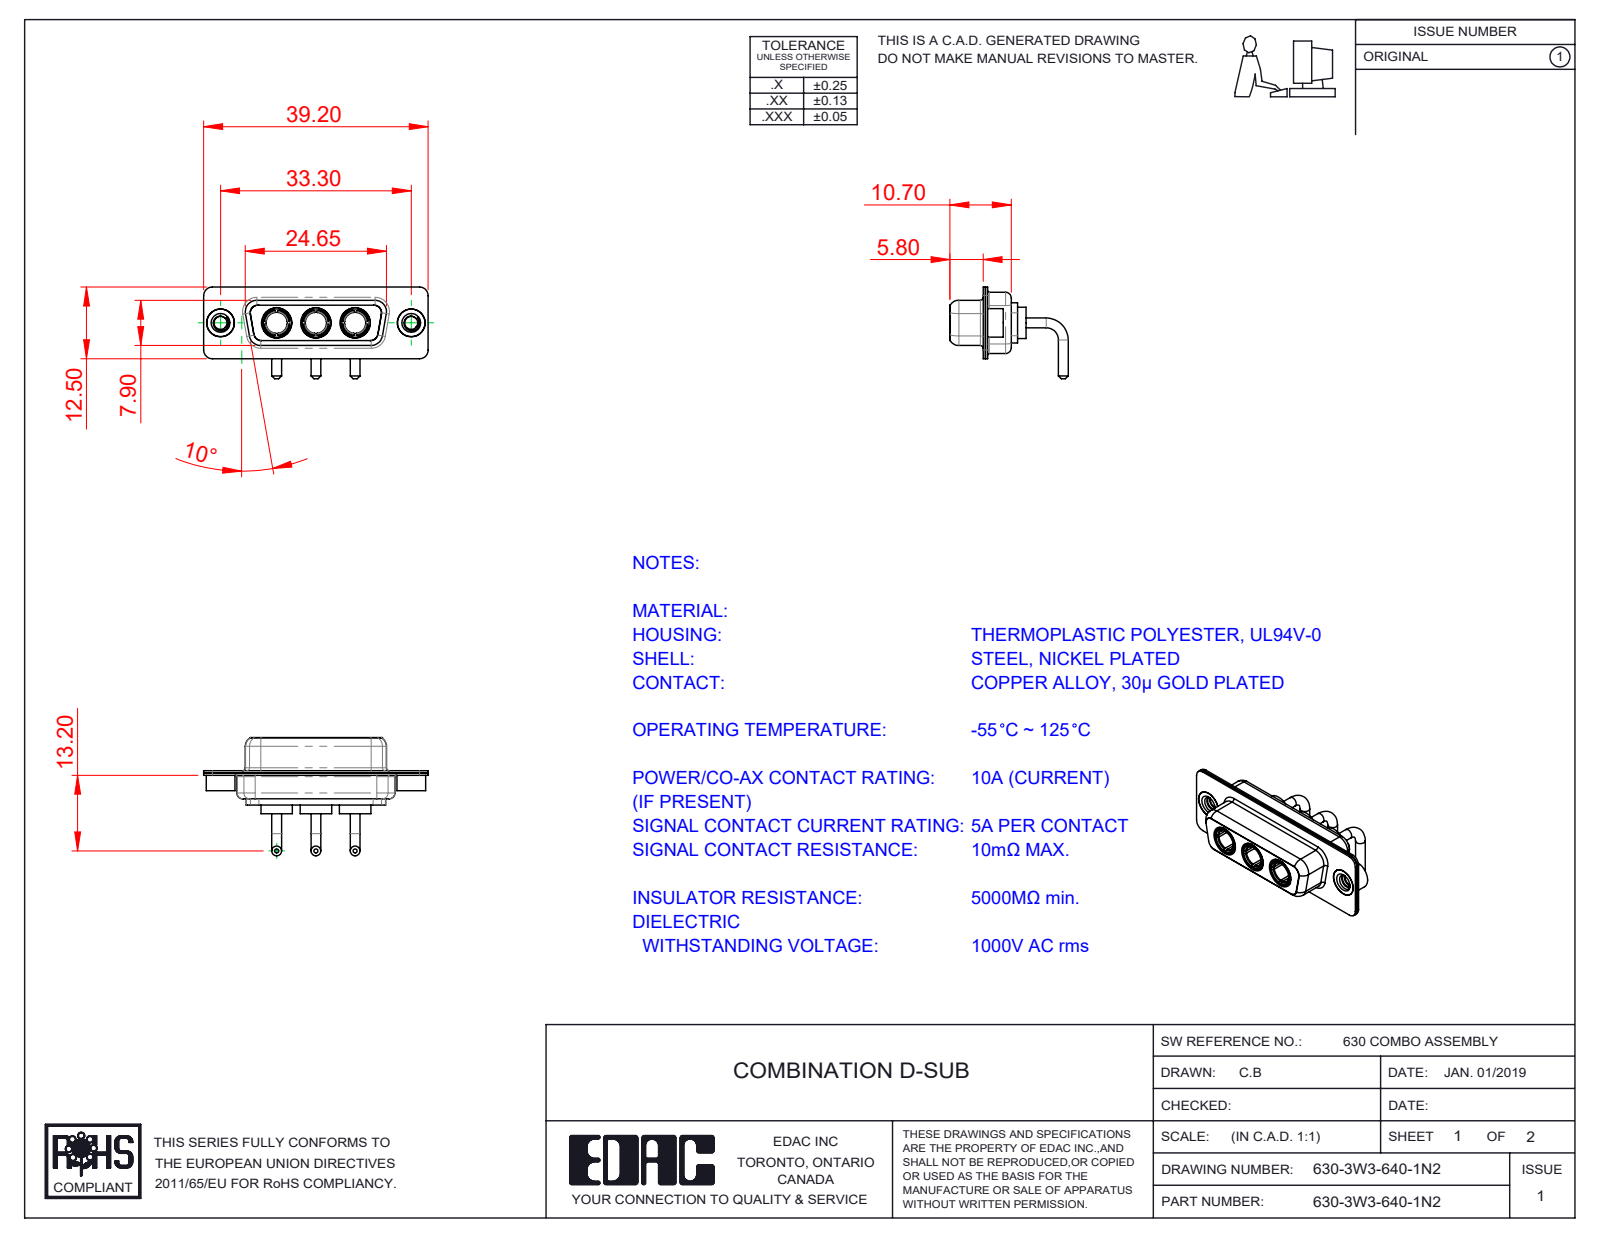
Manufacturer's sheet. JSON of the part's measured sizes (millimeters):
{"part_name": "630Combo Shell Rear_15 Contacts; 630Combo Shell Front_15 Contacts; 630Combo Threaded Rivet_2; Power Socket_10A RA (+2 more)", "step_written_by": "SolidWorks 2020 (CONFIG_CONTROL_DESIGN)", "units": "millimeters", "bodies": {"solids": 11, "faces": 513, "planar": 154, "cylindrical": 212, "other": 147}, "overall_size": [39.2, 20.65, 16], "volume_mm3": 2470, "surface_area_mm2": 5773, "round_holes": [[4.85, 5], [3.7, 3], [5.3, 3], [2.26, 2], [4, 2], [4.05, 2]], "round_bosses_or_shafts": [[1.7, 6], [5.5, 3], [5.2, 3], [4.96, 3], [4.75, 3], [3.75, 3], [5, 2], [4.95, 2]], "partial_cylinders_radius": [[1.5, 16], [1.35, 12], [2, 12], [1.6, 8], [0.25, 4], [0.5, 4], [0.6, 4], [0.65, 4]], "face_to_face_distances": [0.4, 1.4, 0.45, 8.45, 8.9, 1.8, 7.05, 7.5, 0.8, 6.2], "hole_center_spacings": [6.85, 9.8, 16.65, 23.5, 13.7, 33.3]}
